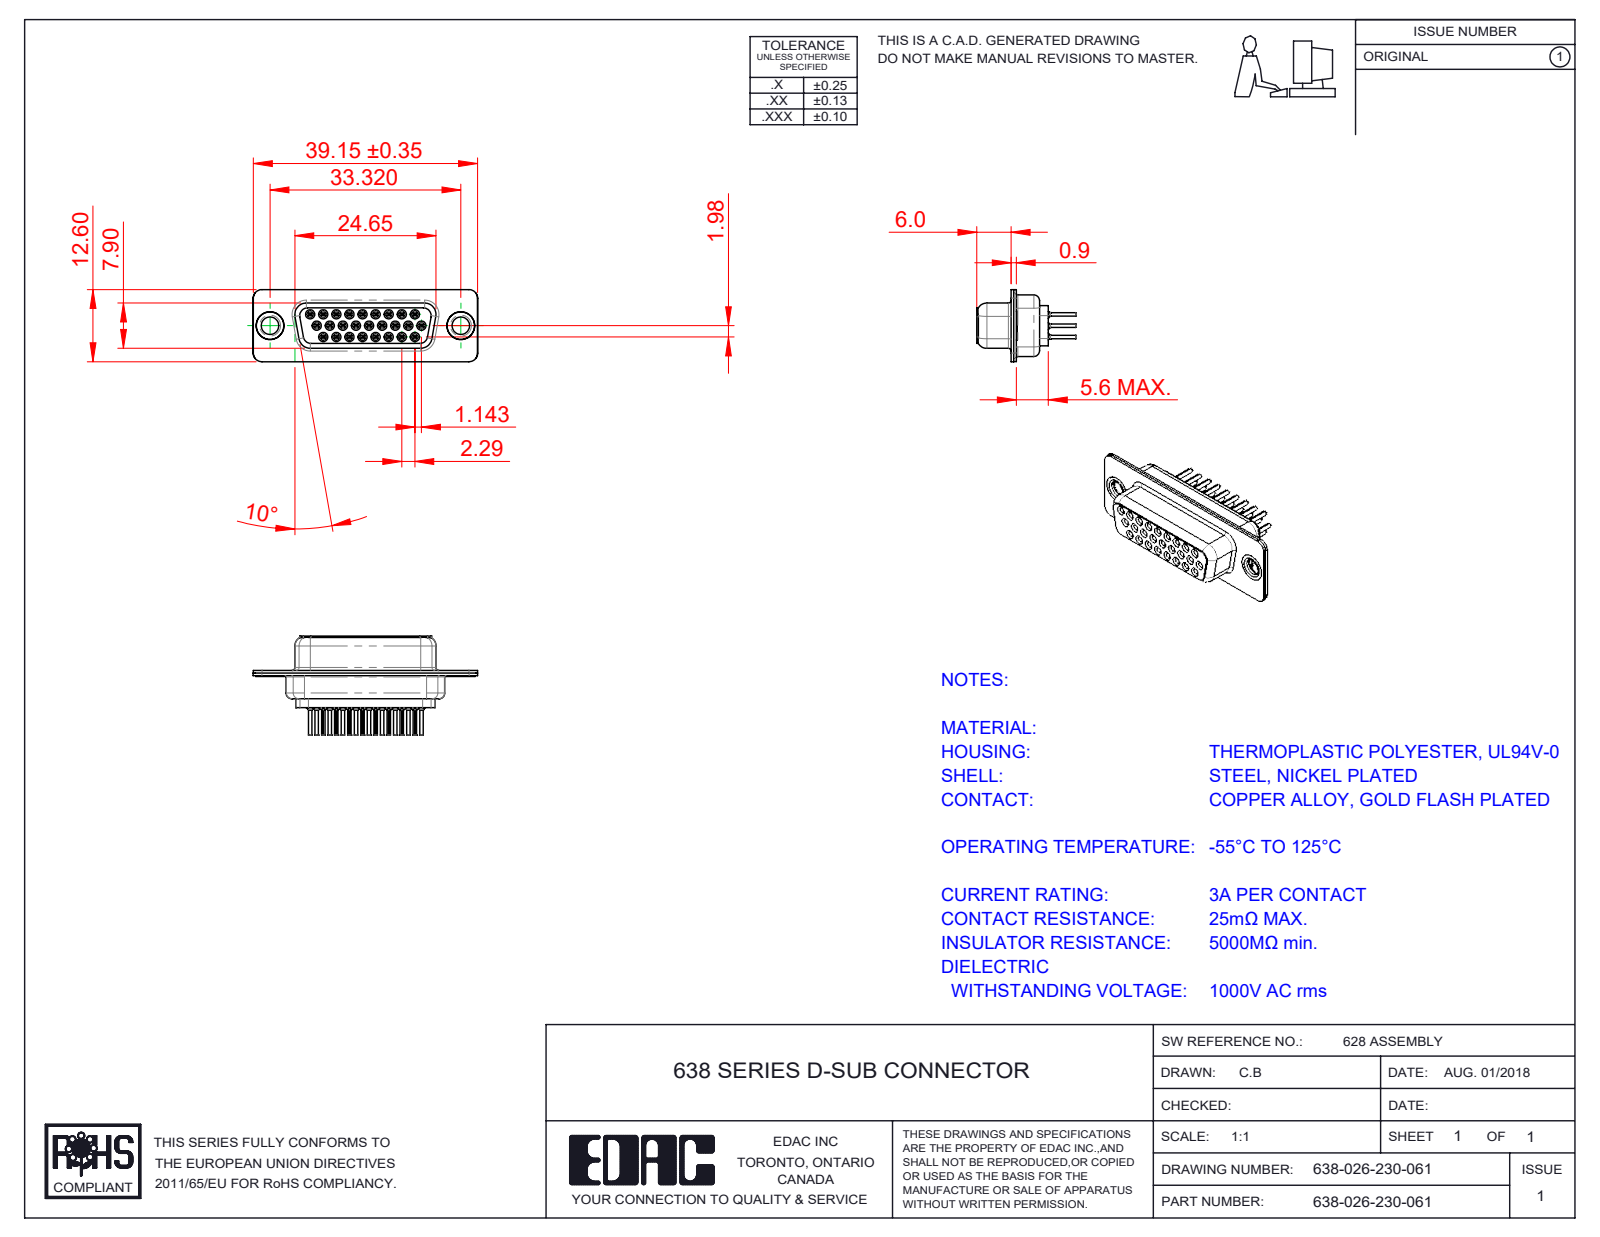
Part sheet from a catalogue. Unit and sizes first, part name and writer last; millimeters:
Units: millimetres
Overall size (bounding box): 39.19 × 17.3 × 12.6
Round holes (diameter × count): ⌀0.2 ×26, ⌀0.8 ×26, ⌀1 ×26, ⌀1.1 ×26, ⌀1.6 ×26, ⌀1.7 ×26, ⌀1.8 ×26, ⌀3.05 ×2, ⌀4 ×2, ⌀4.05 ×2, ⌀4.85 ×2
Round bosses / shafts (diameter × count): ⌀2 ×26, ⌀1.5 ×26, ⌀1.2 ×26, ⌀0.6 ×26, ⌀5 ×2, ⌀4.95 ×2, ⌀4.8 ×2, ⌀3.55 ×2
Partial cylindrical surfaces — rounded edges, fillets, slot ends (radius × count): R0.1 ×52, R1.5 ×20, R0.28 ×18, R2 ×12, R1.55 ×8, R1.35 ×5, R0.25 ×4, R0.5 ×4
Main face-to-face distances: 0.45, 0.4, 1.43, 8.88, 0.9, 6.6, 2.28, 1.4, 7.05, 0.85
Hole centre spacings: 3.96, 2.28, 4.57, 6.05, 2.29, 8.24, 6.86, 10.48
Volume: 2 135 mm³ · Surface area: 8 161 mm²
Bodies: 31 solids, 3555 faces (873 planar, 979 cylindrical, 1703 other)
Part name (STEP PRODUCT): 638-026-230-061; 638 Shell Front_26 Contacts; 638 Contact Row 2_30; 638 Contact Row 3_30 (+4 more)
STEP written by: SolidWorks 2020 (CONFIG_CONTROL_DESIGN)
